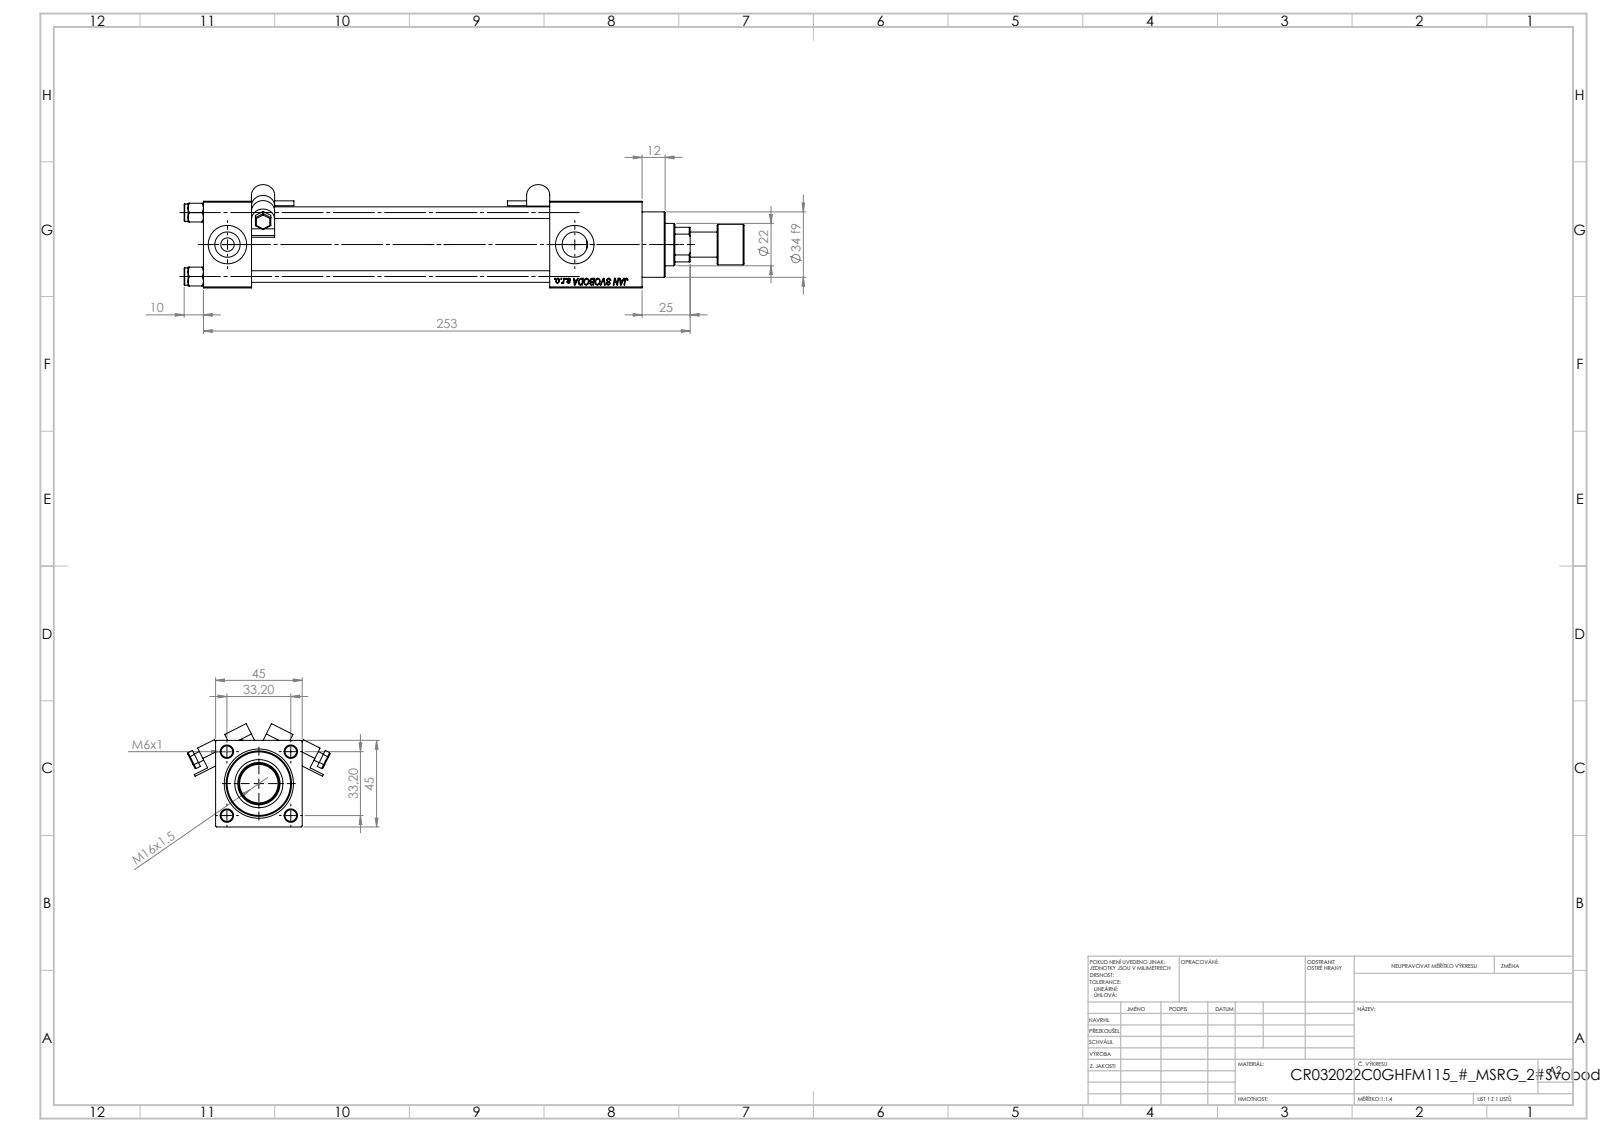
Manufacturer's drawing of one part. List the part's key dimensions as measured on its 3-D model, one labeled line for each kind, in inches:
Part name (STEP PRODUCT): V215_VC_A; V215CR_C_Body; V215CR_VCP_C; MSRF_MSRG1 (+3 more)
STEP written by: SolidWorks 2019 (CONFIG_CONTROL_DESIGN)
Units: inches
Bodies: 14 solids, 1222 faces (564 planar, 118 cylindrical, 540 other)
Overall size (bounding box): 11.457 × 2.915 × 2.113
Volume: 18.91 in³ · Surface area: 179.7 in²
Round holes (diameter × count): ⌀0.236 ×4, ⌀0.276 ×2, ⌀0.518 ×2, ⌀0.787 ×2, ⌀0.413 ×1, ⌀0.866 ×1, ⌀0.945 ×1, ⌀0.984 ×1, ⌀1.26 ×1, ⌀1.299 ×1
Round bosses / shafts (diameter × count): ⌀0.354 ×4, ⌀0.197 ×2, ⌀0.098 ×2, ⌀1.496 ×1, ⌀1.339 ×1, ⌀0.827 ×1, ⌀0.512 ×1
Partial cylindrical surfaces — rounded edges, fillets, slot ends (radius × count): R0.02 ×12, R0.236 ×4
Main face-to-face distances: 1.772, 0.984, 7.087, 6.102, 8.976, 7.992, 1.89, 7.846, 6.862, 0.76
Hole centre spacings: 0.924, 1.307, 1.848, 7.106
